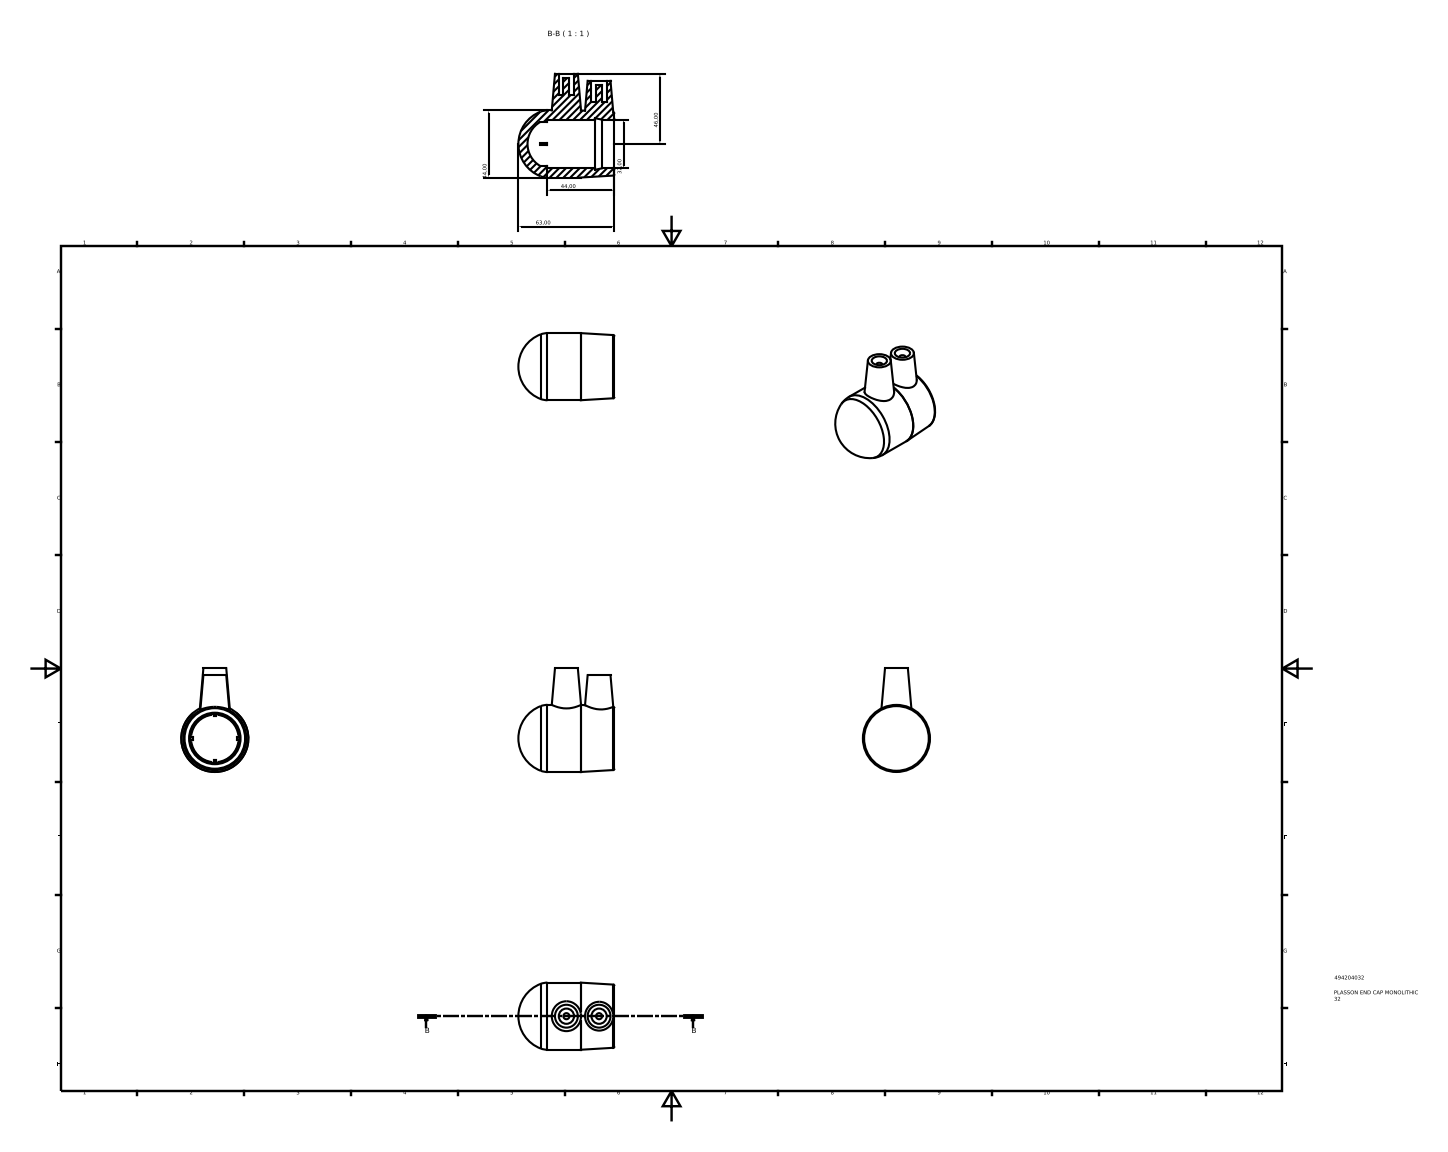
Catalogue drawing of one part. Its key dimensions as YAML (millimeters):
part_name: "494204032"
step_written_by: "Autodesk Inventor 2015 (AUTOMOTIVE_DESIGN)"
units: millimeters
bodies: {solids: 1, faces: 48, planar: 24, cylindrical: 8, other: 16}
overall_size: [68, 63, 44]
volume: 49648
surface_area: 18502
round_holes:
  - {diameter: 10, count: 2}
  - {diameter: 32, count: 1}
  - {diameter: 44, count: 1}
round_bosses_or_shafts:
  - {diameter: 4, count: 2}
face_to_face_distances: [4.6, 14, 12.6, 18.6, 9.4, 1.6, 13.6, 15.2, 11, 3]
hole_center_spacings: [21.42]
